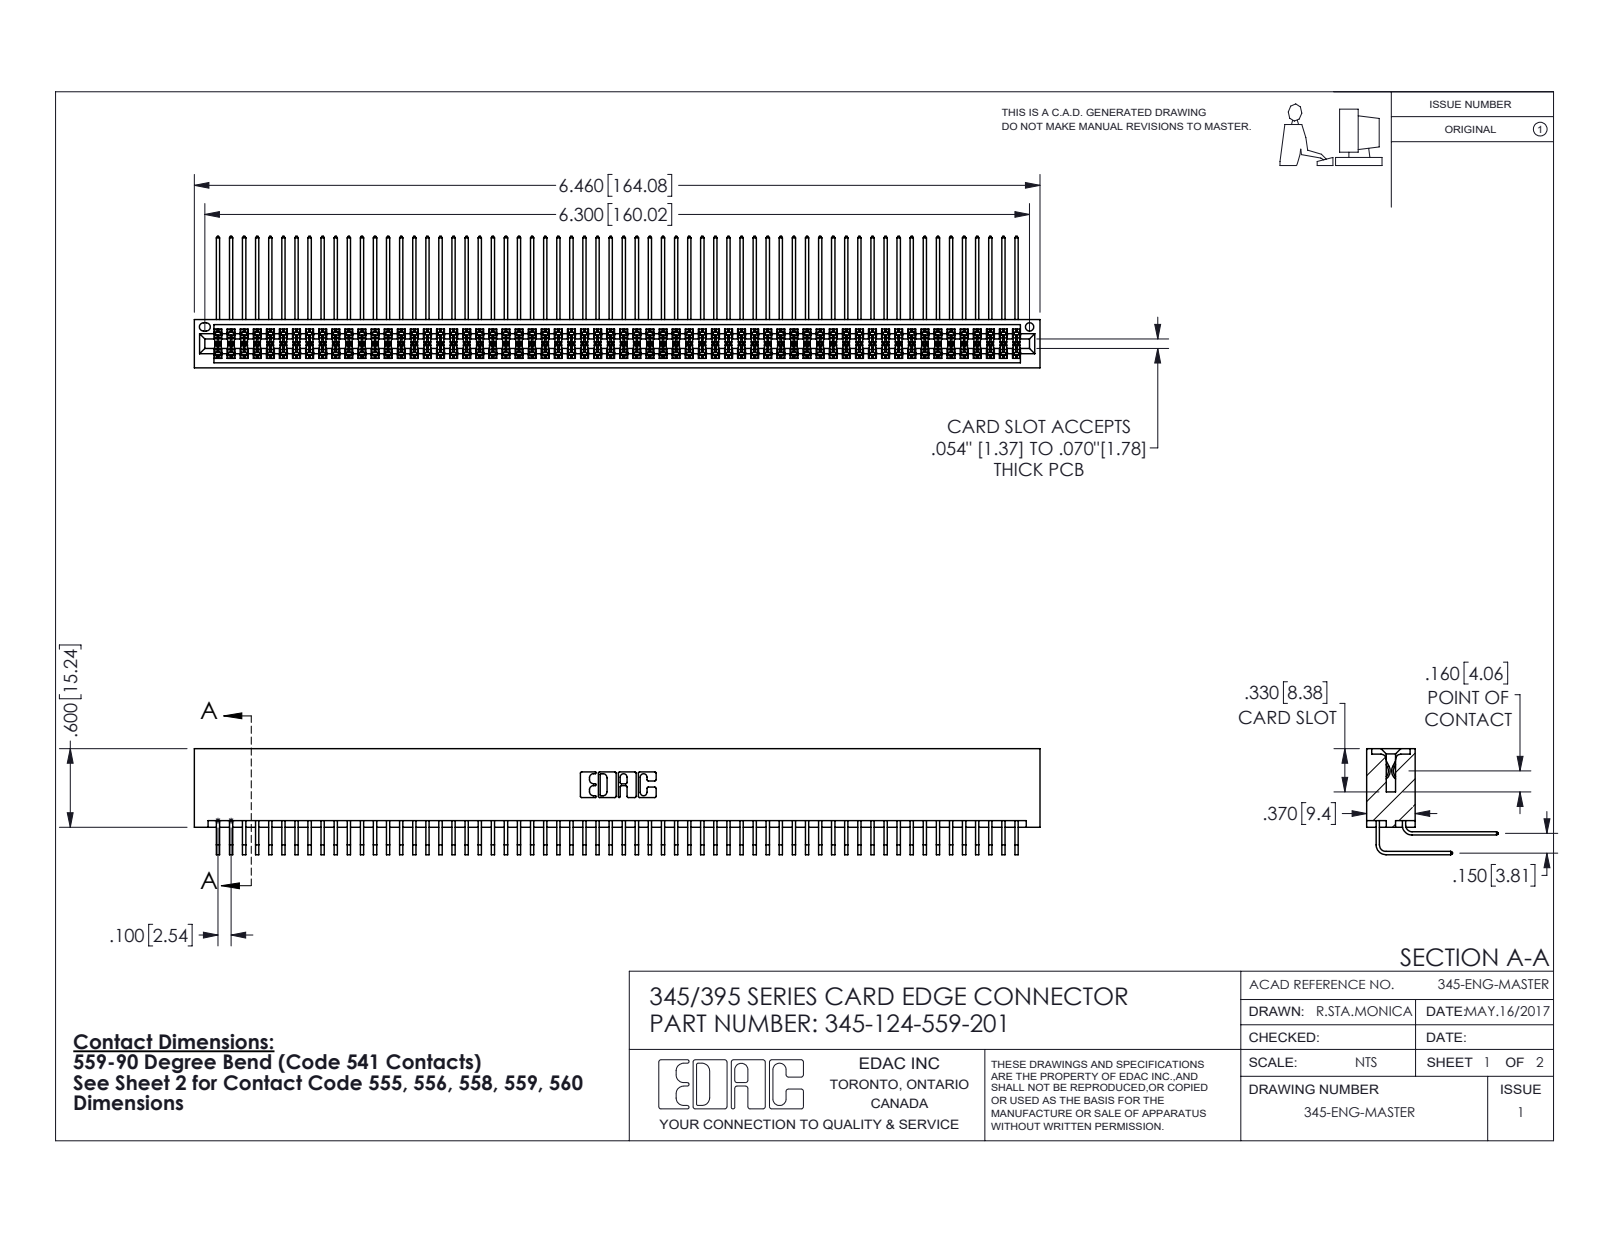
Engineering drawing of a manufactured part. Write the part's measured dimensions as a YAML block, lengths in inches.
part_name: "345 Part_No Mounting Lugs; 345-124-559-201; 345-292-001_558 559 Tail - 1; 345-292-001_559 Tail - 2"
step_written_by: "SolidWorks 2016 (CONFIG_CONTROL_DESIGN)"
units: inches
bodies: {solids: 125, faces: 6566, planar: 4416, cylindrical: 2150, other: 0}
overall_size: [6.46, 1.005, 0.809]
volume: 1.065
surface_area: 46.28
round_holes:
  - {diameter: 0.064, count: 1}
partial_cylinders:
  - {radius: 0.006, count: 248}
  - {radius: 0.01, count: 22}
  - {radius: 0.007, count: 6}
  - {radius: 0.031, count: 6}
  - {radius: 0.026, count: 3}
  - {radius: 0.014, count: 2}
  - {radius: 0.019, count: 2}
  - {radius: 0.022, count: 2}
face_to_face_distances: [0.072, 0.298, 0.2, 0.37, 0.098, 0.272, 0.025, 0.225, 0.175, 0.15]
